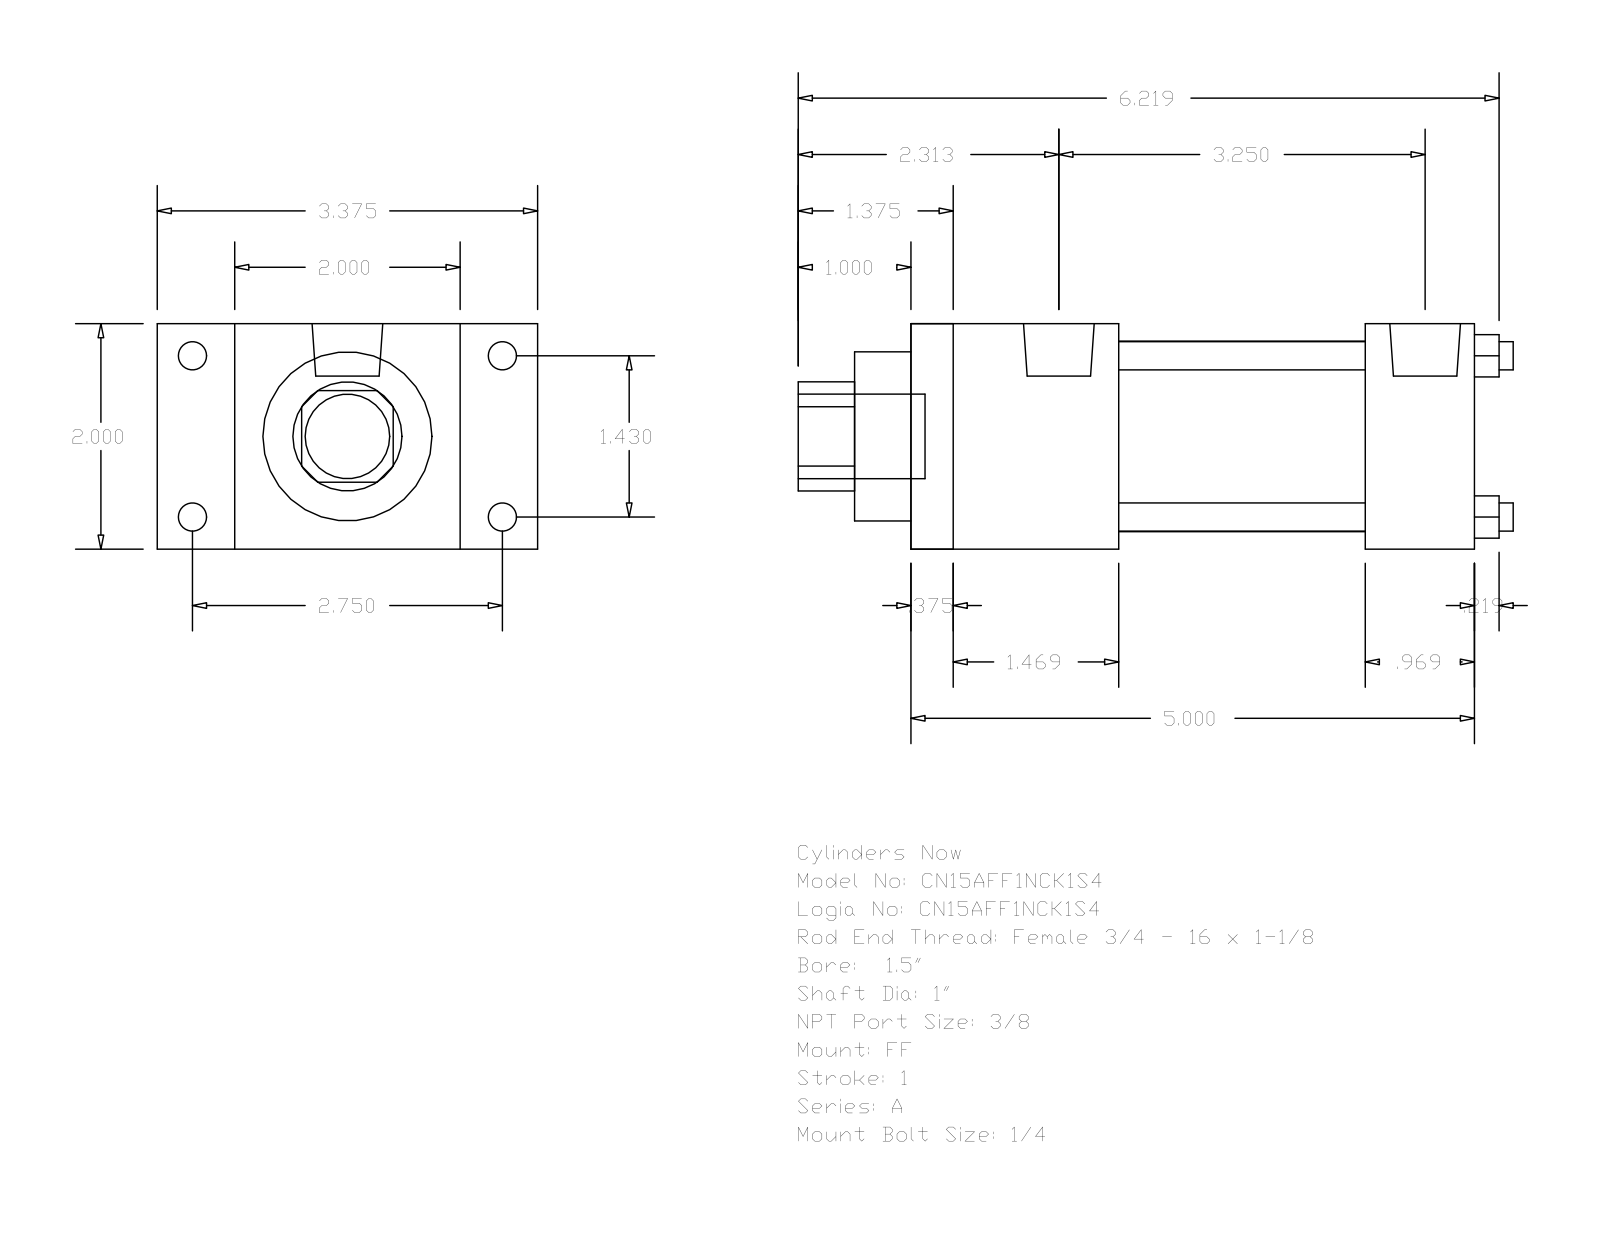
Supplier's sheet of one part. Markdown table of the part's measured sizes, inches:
| quantity | value |
| --- | --- |
| part name | A_FF__0150_1 |
| STEP written by | GSSL Pune (CONFIG_CONTROL_DESIGN) |
| units | inches |
| bodies | 0 solids, 92 faces (64 planar, 28 cylindrical, 0 other) |
| overall size | 6.344 × 3.375 × 2 |
| round holes (diameter × count) | 0.25 × 4, 1 × 1, 1.5 × 1, 1.69 × 1 |
| round bosses / shafts (diameter × count) | 0.25 × 4, 0.219 × 4, 0.627 × 2, 0.75 × 1 |
| partial cylindrical surfaces (radius × count) | 0.484 × 1 |
| main face-to-face distances | 2, 5, 0.375, 4.625, 1.844, 4.031, 1.469, 3.656, 2.187, 3.156 |
| hole center spacings | 1.011, 1.43, 2.022 |
